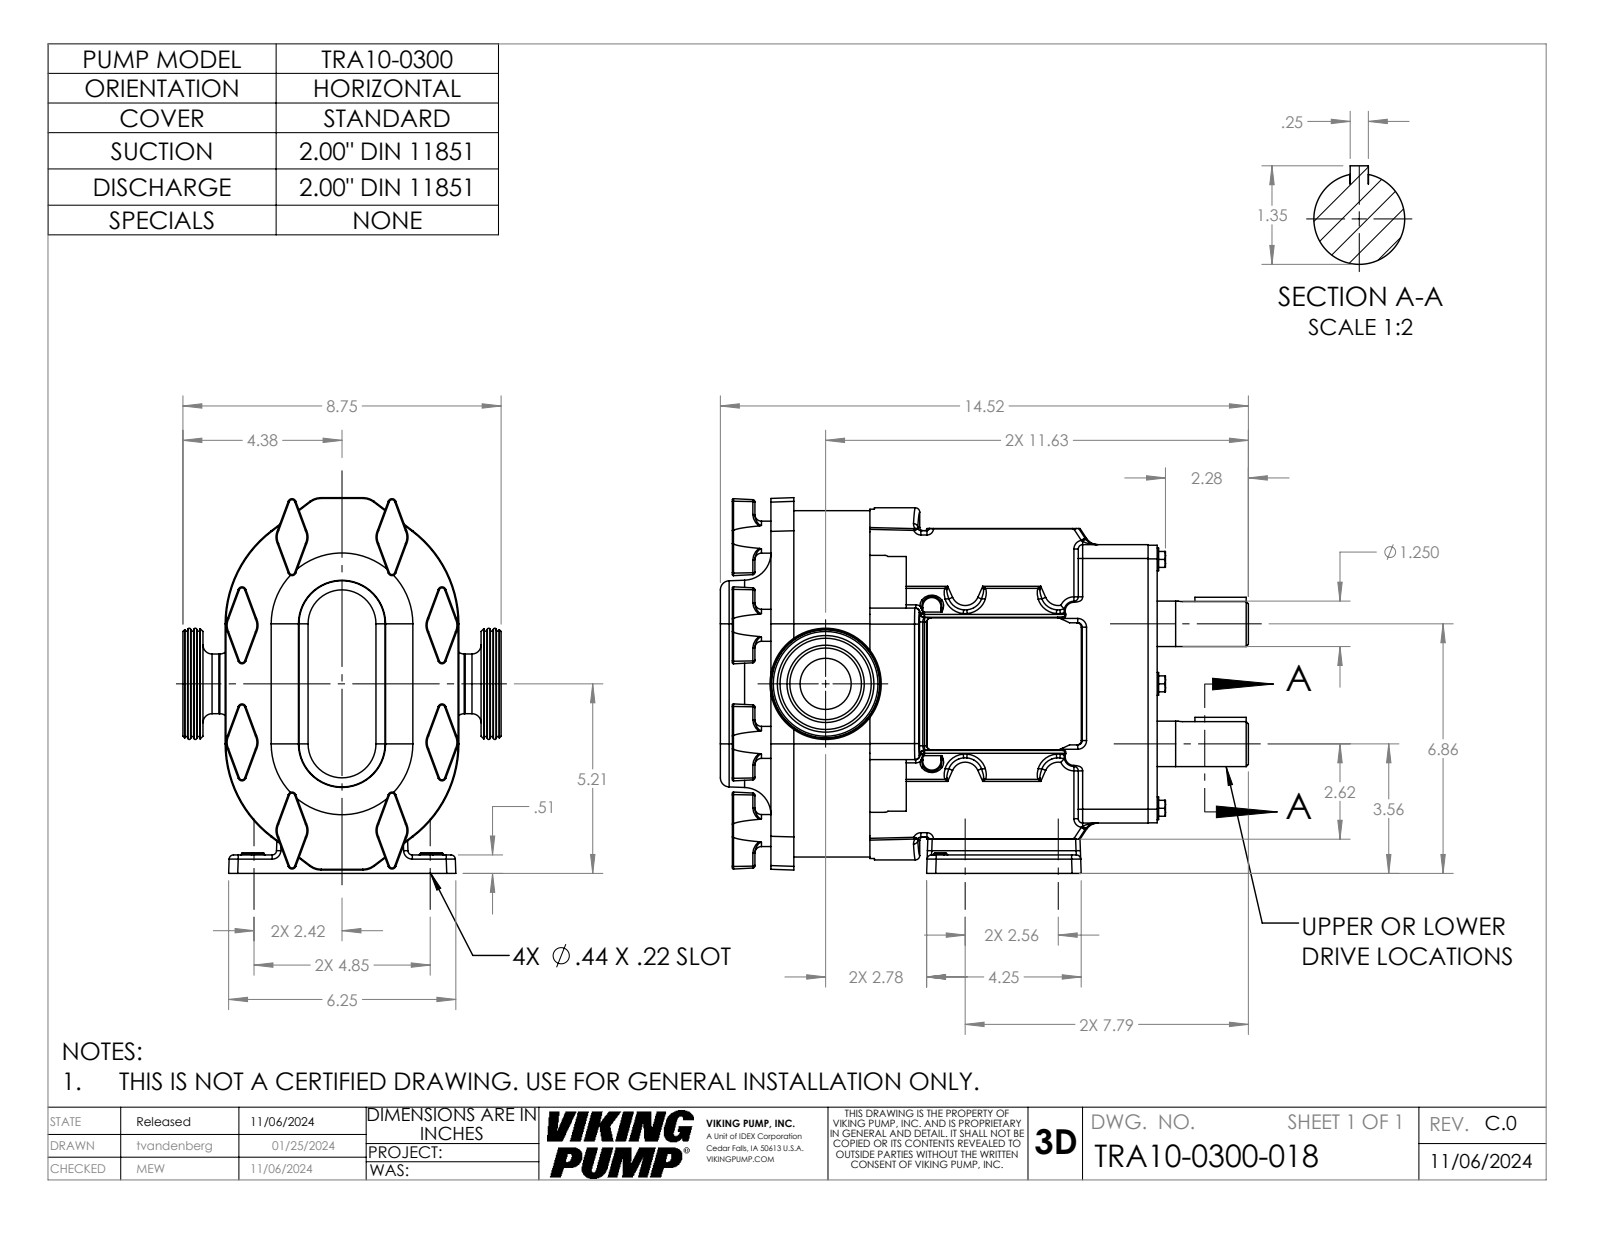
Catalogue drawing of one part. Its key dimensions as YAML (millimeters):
part_name: "TRA10-0300-GEARBOX-H; TRA10-0300-BODY; TRA10-0300-018; TRA10-0300-COVER-STD (+1 more)"
step_written_by: "SolidWorks 2023 (AUTOMOTIVE_DESIGN)"
units: millimeters
bodies: {solids: 5, faces: 1158, planar: 287, cylindrical: 353, other: 518}
overall_size: [368.81, 262.34, 222.25]
volume: 7585000
surface_area: 498961
round_holes:
  - {diameter: 35.71, count: 1}
  - {diameter: 63.7, count: 1}
round_bosses_or_shafts:
  - {diameter: 22.35, count: 8}
  - {diameter: 15.88, count: 6}
  - {diameter: 31.72, count: 2}
  - {diameter: 54, count: 1}
  - {diameter: 41.66, count: 1}
partial_cylinders:
  - {radius: 3.05, count: 90}
  - {radius: 0.76, count: 50}
  - {radius: 1.52, count: 44}
  - {radius: 2.29, count: 10}
  - {radius: 5.56, count: 8}
  - {radius: 9.53, count: 8}
  - {radius: 9.65, count: 8}
  - {radius: 12.7, count: 8}
face_to_face_distances: [53.14, 253.8, 200.66, 20.53, 112.57, 25.4, 78.54, 175.26, 7.77, 125.33]
